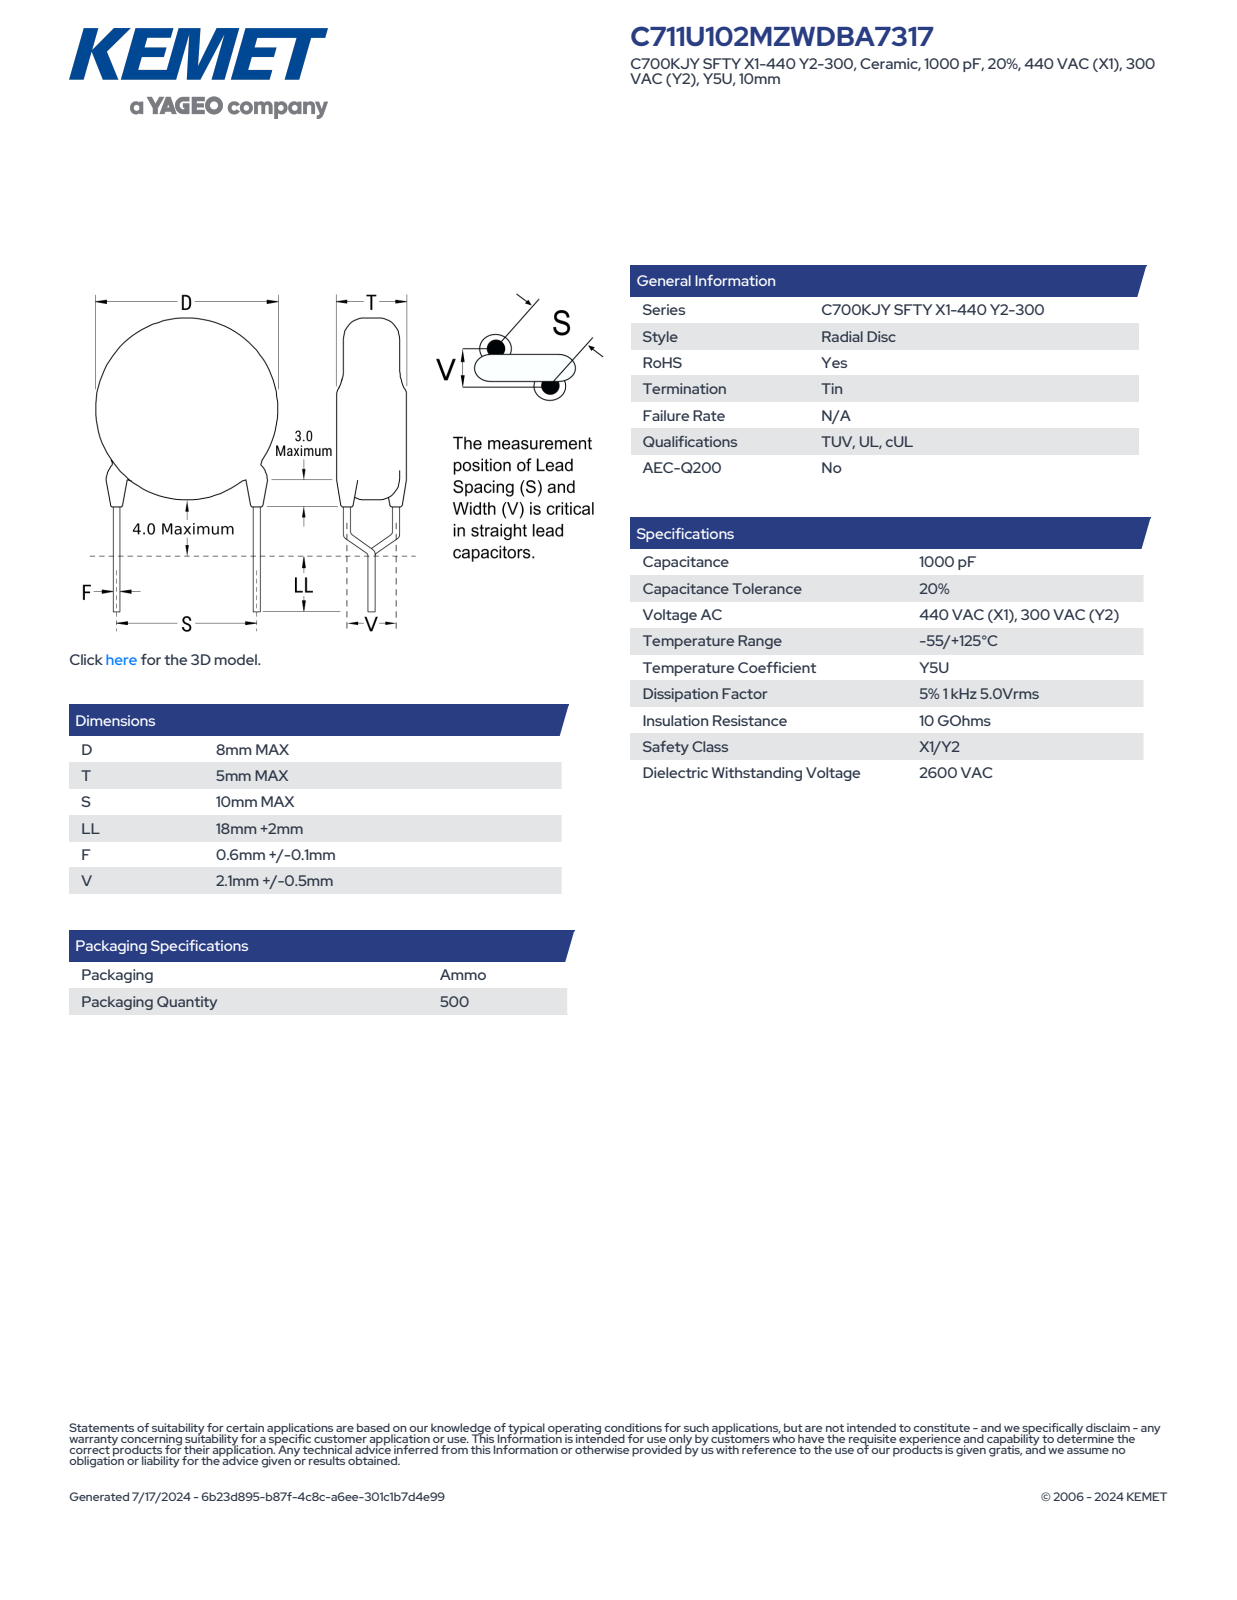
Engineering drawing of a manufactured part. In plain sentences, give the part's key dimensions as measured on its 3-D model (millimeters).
The part is named "CCD_VC8X5_D8T5S10LL20F0.7V2.1". Its 3-D file was written by "SolidWorks 2021 (AUTOMOTIVE_DESIGN)". It is 4 solids with 89 faces: 63 planar, 22 cylindrical and 4 other. Overall it measures 28 by 11.2 by 5 millimeters. Its volume is 263 cubic millimeters and its surface area 321 square millimeters. Round bosses or shafts: 6 of diameter 0.7, 4 of diameter 1.2, 1 of diameter 8. The main face-to-face distances are 5, 20, 0.97, 24.63, 4.63, 23.66, 3.66, 0.36, 0.78, 0.35.
